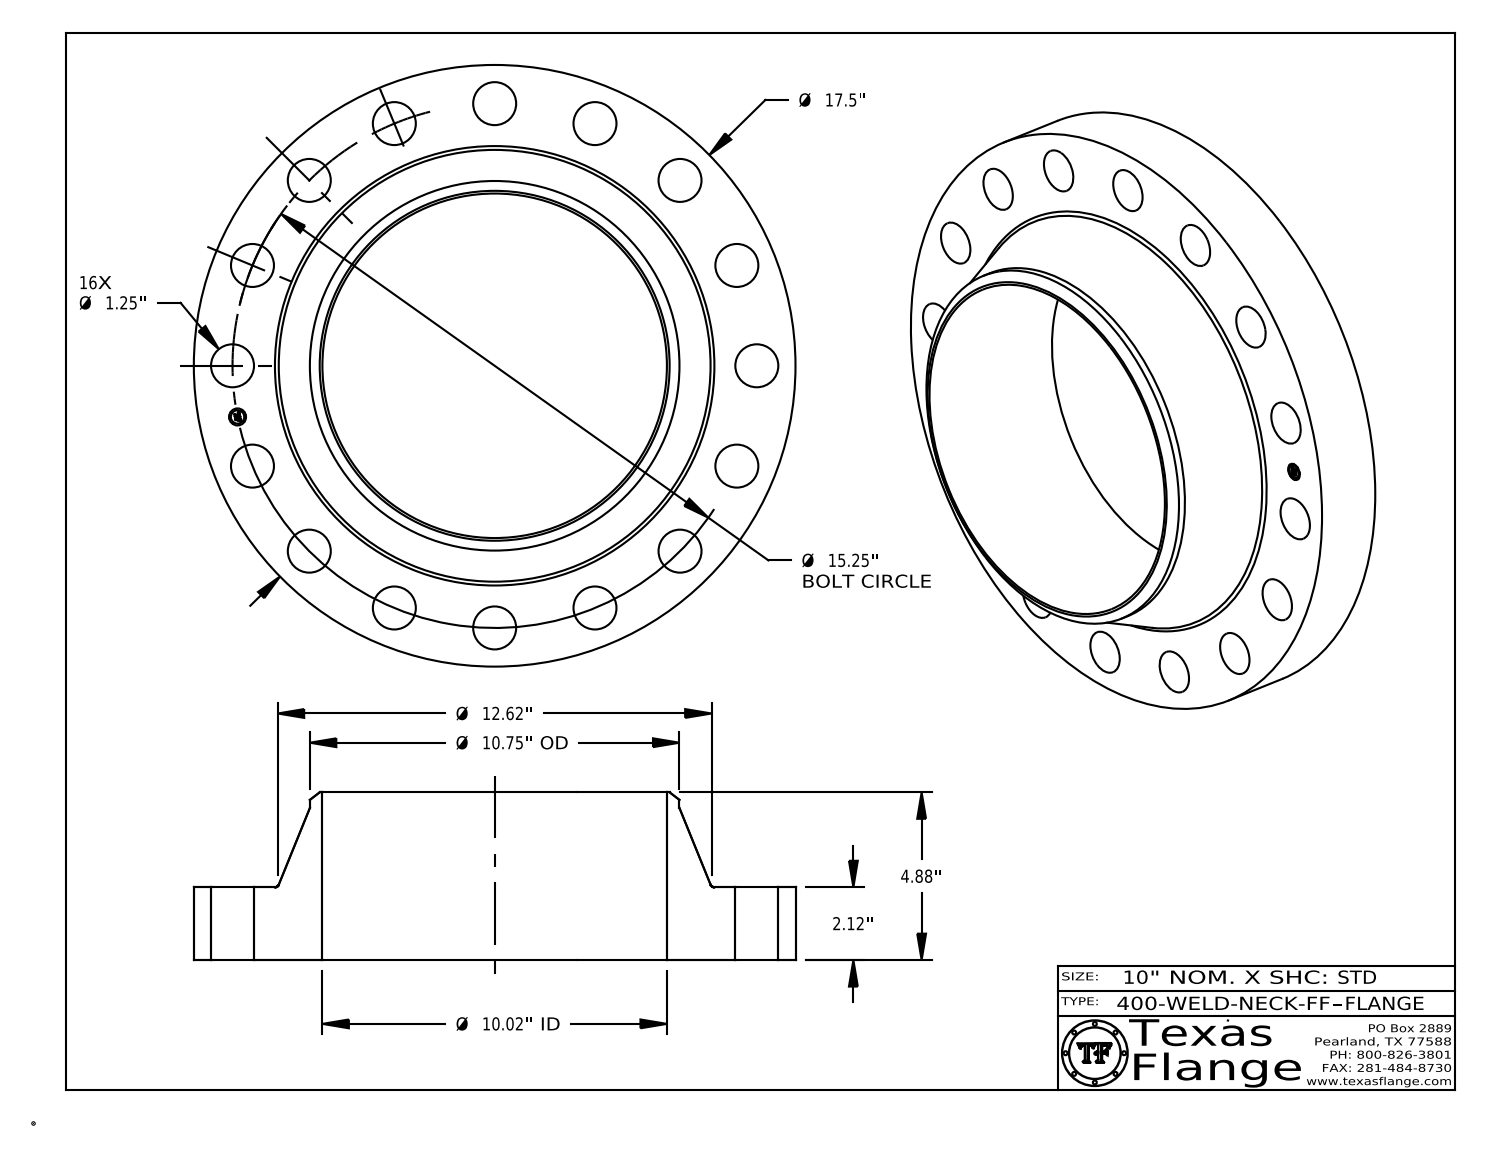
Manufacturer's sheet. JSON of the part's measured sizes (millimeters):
{"part_name": "400-WELD-NECK-FF", "step_written_by": "CATIA V5 STEP AP214 (AUTOMOTIVE_DESIGN)", "units": "millimeters", "bodies": {"solids": 1, "faces": 432, "planar": 368, "cylindrical": 58, "other": 6}, "overall_size": [444.5, 444.5, 124], "volume_mm3": 6088000, "surface_area_mm2": 486600, "round_holes": [[31.8, 16], [12.6, 1], [254.5, 1]], "round_bosses_or_shafts": [[0.8, 8], [444.5, 1], [273.1, 1], [9.9, 1]], "face_to_face_distances": [53.8, 124, 70.1, 0.4, 53.5, 70.5, 3.8, 3.7, 0.7, 2.4], "hole_center_spacings": [215.2, 273.9, 379.9, 357.9, 193.7, 75.6, 75.6, 148.2]}
